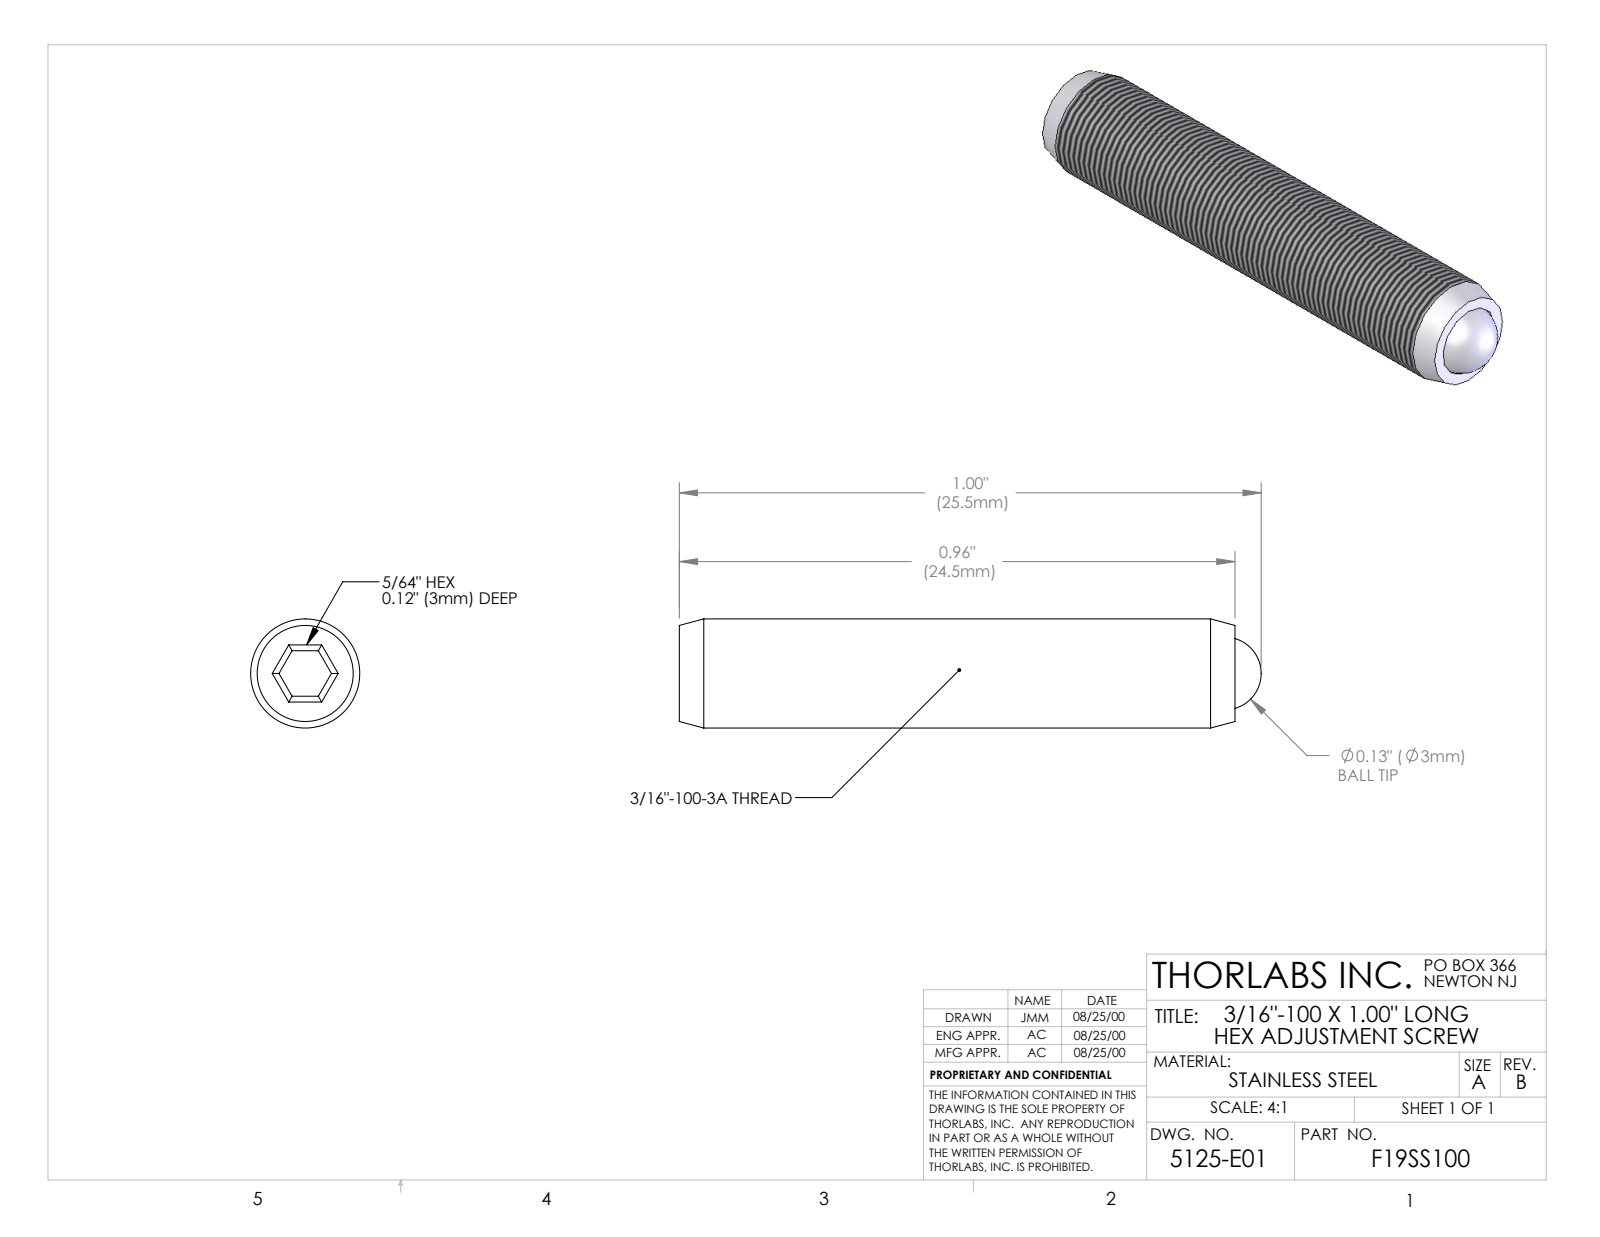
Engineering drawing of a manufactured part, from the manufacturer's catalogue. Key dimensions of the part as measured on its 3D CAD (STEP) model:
Part name (STEP PRODUCT): 5125-E0W
STEP written by: SolidWorks 2007 (AUTOMOTIVE_DESIGN)
Units: millimetres
Bodies: 2 solids, 29 faces (15 planar, 4 cylindrical, 10 other)
Overall size (bounding box): 25.4 × 4.76 × 4.76
Volume: 421 mm³ · Surface area: 456 mm²
Round holes (diameter × count): ⌀3.19 ×1
Round bosses / shafts (diameter × count): ⌀4.76 ×1
Main face-to-face distances: 1.98, 24.26, 3.05, 21.21, 1.99
